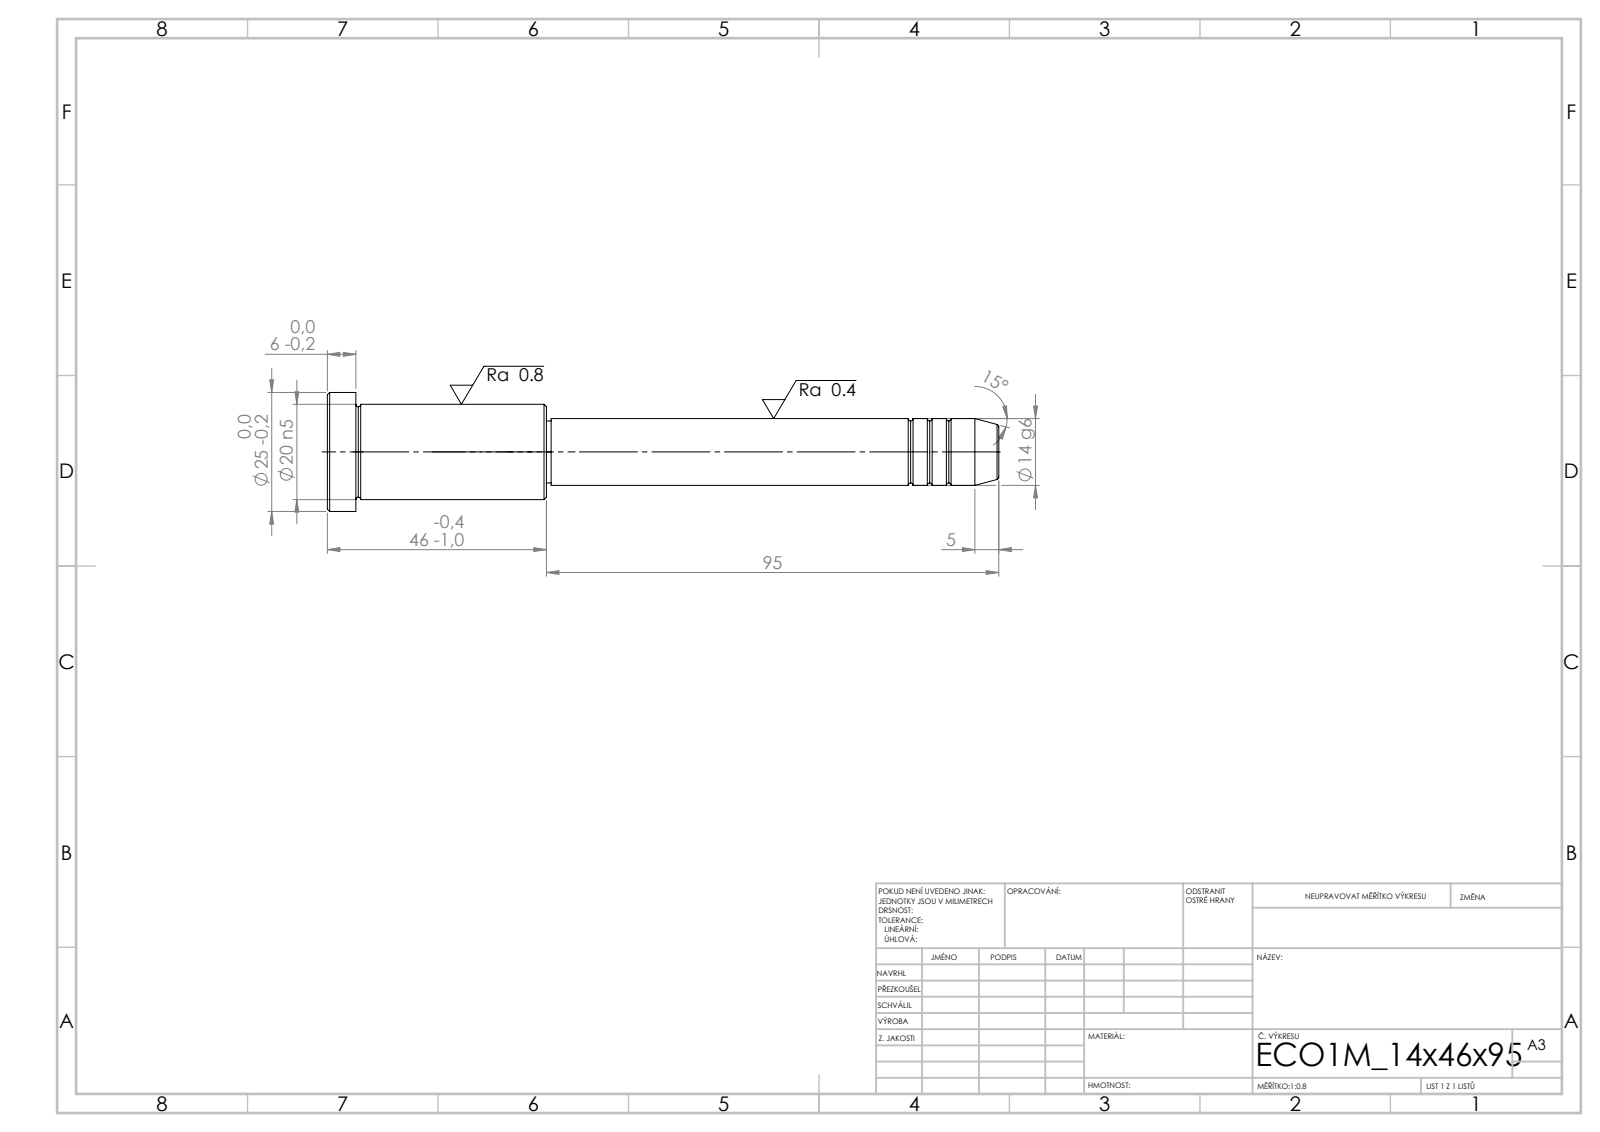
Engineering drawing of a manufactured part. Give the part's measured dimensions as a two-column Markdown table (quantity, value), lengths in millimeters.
| quantity | value |
| --- | --- |
| STEP written by | SolidWorks 2019 (CONFIG_CONTROL_DESIGN) |
| units | millimeters |
| bodies | 1 solid, 43 faces (5 planar, 14 cylindrical, 24 other) |
| overall size | 141 × 25 × 25 |
| volume | 29 884 mm³ |
| surface area | 8 169 mm² |
| round bosses / shafts (diameter × count) | 25 × 1, 20 × 1, 14 × 1, 13 × 1 |
| main face-to-face distances | 6, 40, 46, 95, 135, 141, 94, 1, 41, 47 |
